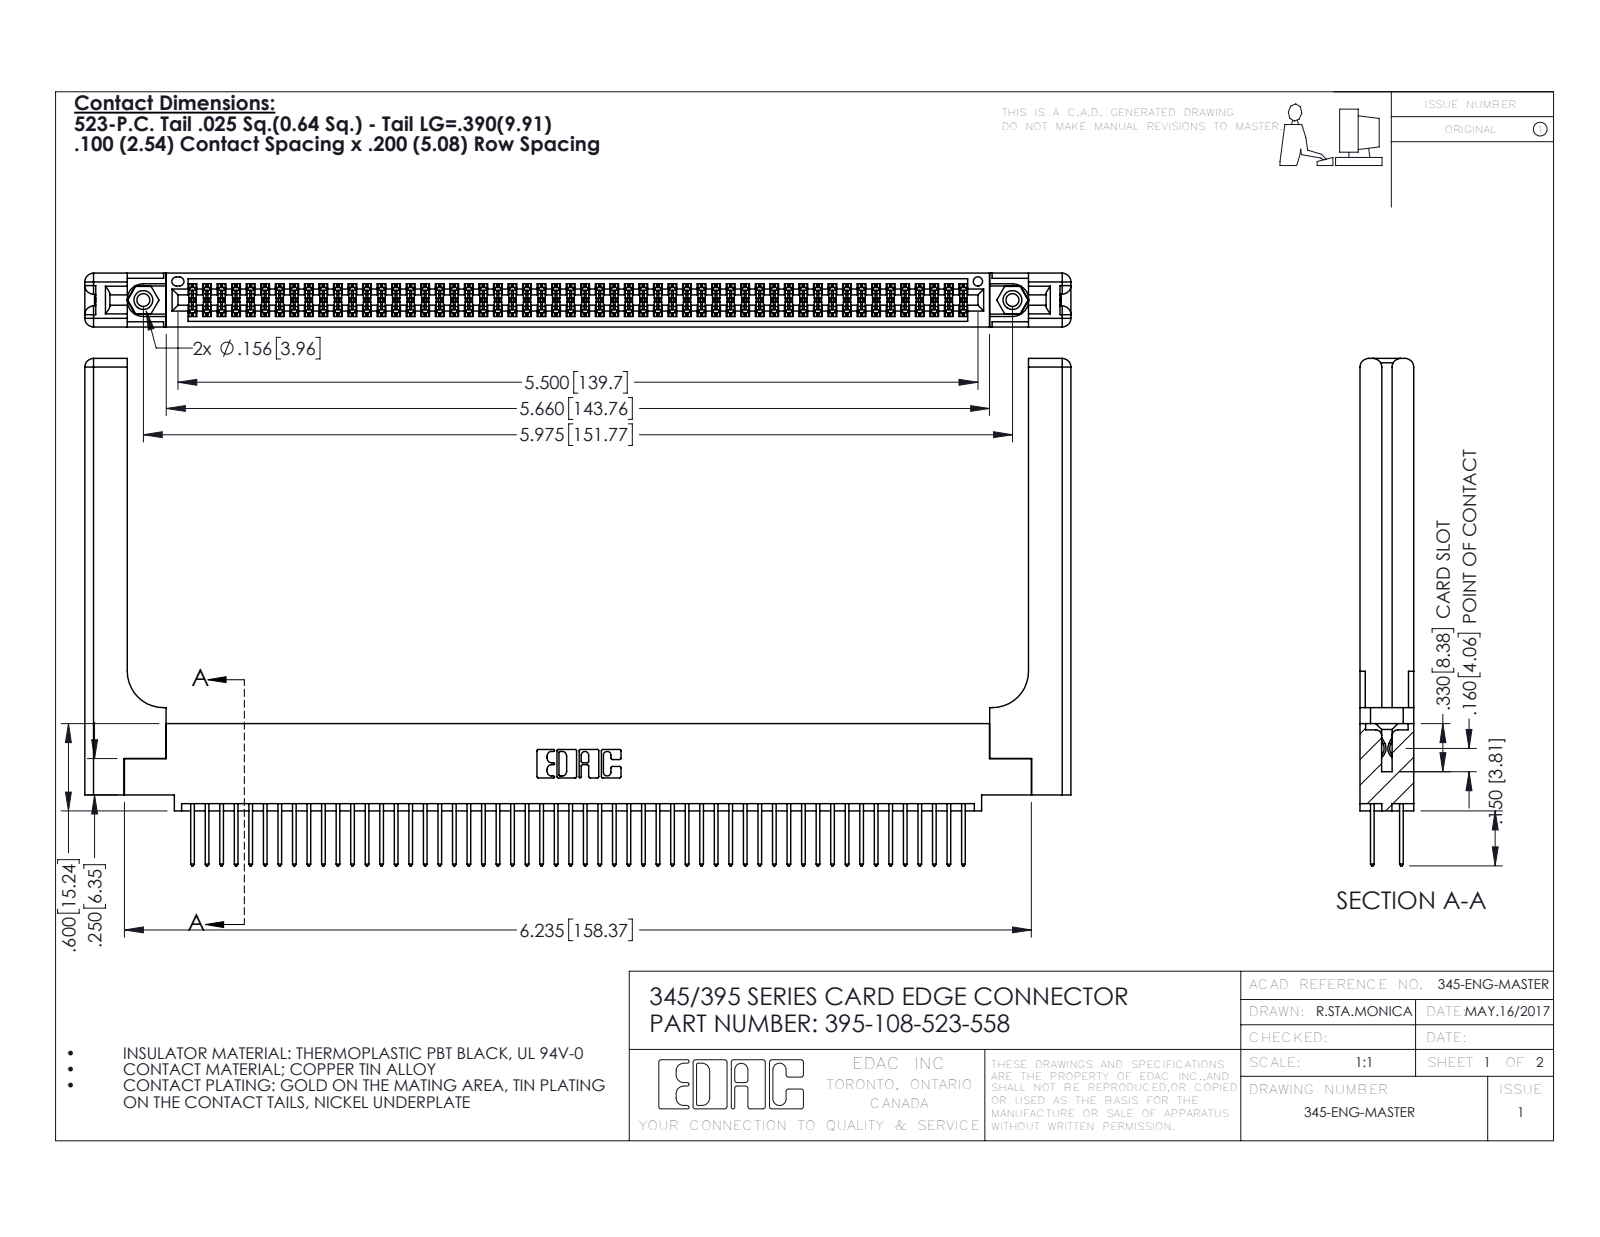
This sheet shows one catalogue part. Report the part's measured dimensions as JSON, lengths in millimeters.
{"part_name": "345 Part_0.110 Offset - 0.156 Dia-TH; 345-250-001_345-250-001-102; 345-292-001_345-293-123; 395-108-523-558 (+1 more)", "step_written_by": "SolidWorks 2016 (CONFIG_CONTROL_DESIGN)", "units": "millimeters", "bodies": {"solids": 113, "faces": 5786, "planar": 3796, "cylindrical": 1930, "other": 60}, "overall_size": [172.2, 88.6, 9.4], "volume_mm3": 25470, "surface_area_mm2": 31480, "round_holes": [[2.3, 2], [3.2, 2], [4, 2], [1.6, 1]], "round_bosses_or_shafts": [[3.9, 2]], "partial_cylinders_radius": [[0.2, 162], [0.3, 108], [0.3, 22], [1.5, 16], [0.2, 6], [0.8, 6], [0.7, 3], [0.4, 2]], "face_to_face_distances": [1.8, 7.6, 9.4, 2.5, 6.9, 0.6, 5.1, 5.7, 4.4, 3.8], "hole_center_spacings": [6.9, 145.8, 151.8]}
